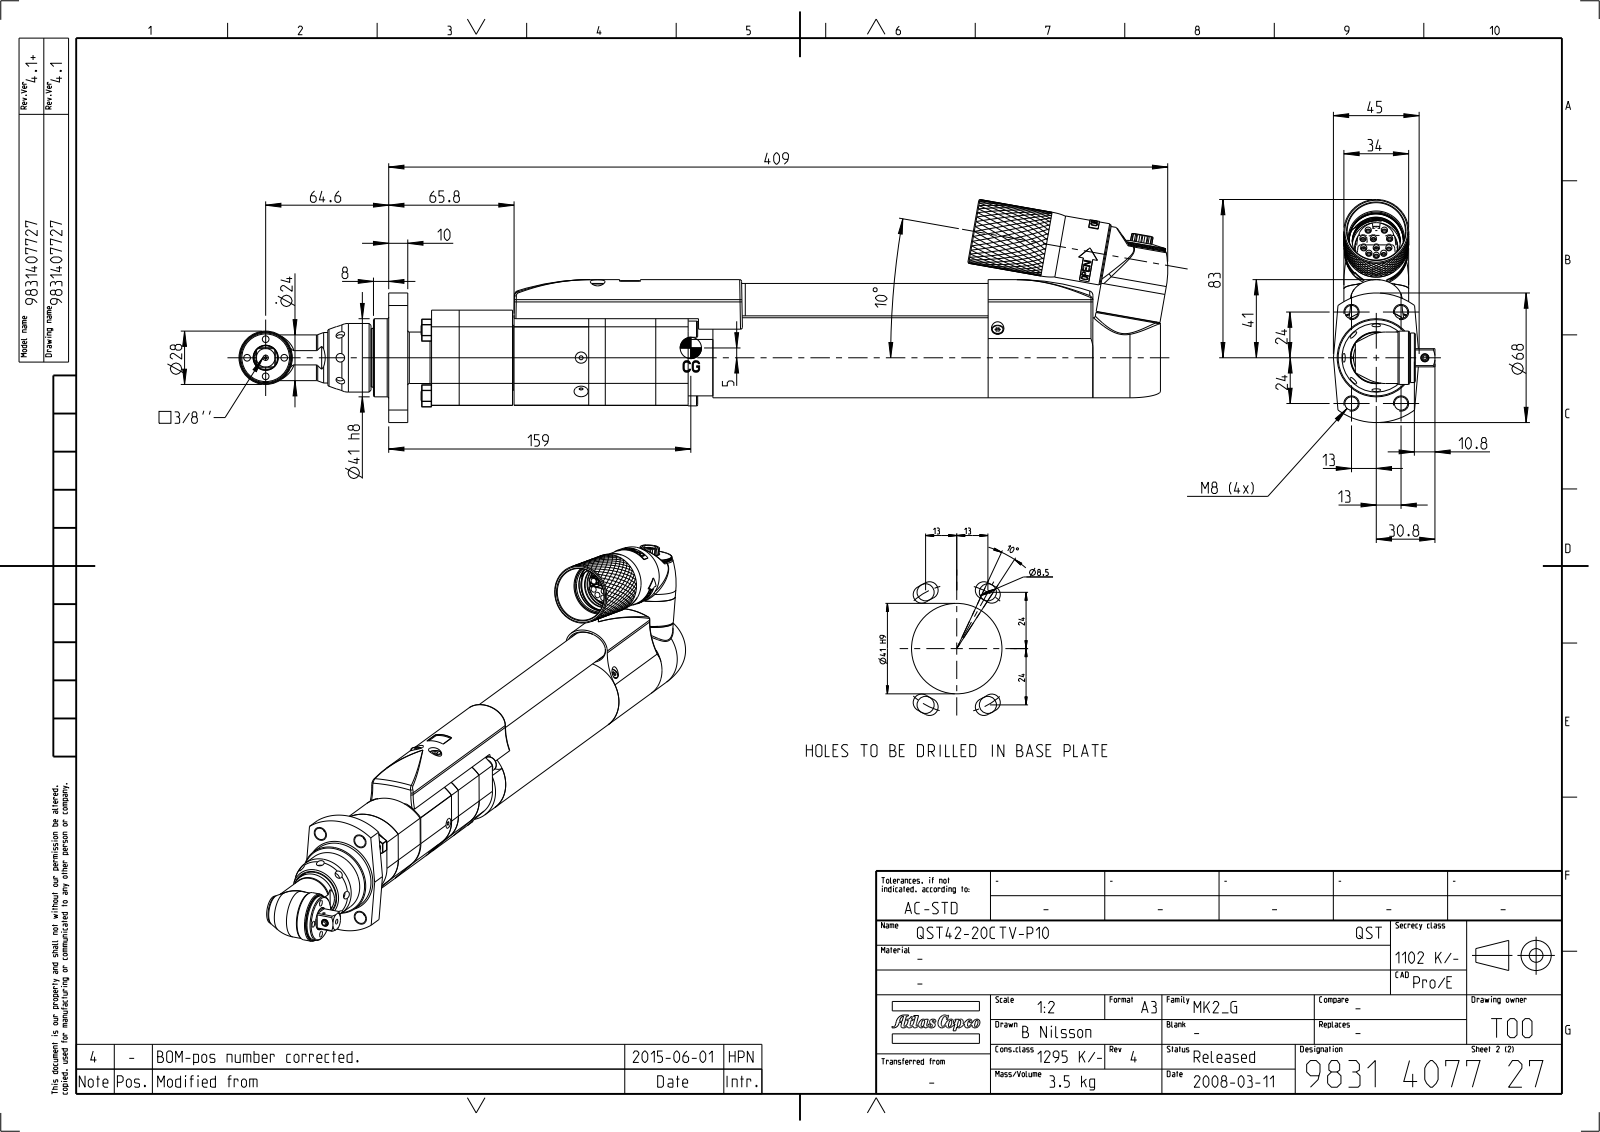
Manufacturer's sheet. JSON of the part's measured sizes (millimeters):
{"part_name": "4230260102; 4230260112_ASM; 4230262500; 0219110017 (+8 more)", "step_written_by": "CREO PARAMETRIC BY PTC INC, 2014500 (CONFIG_CONTROL_DESIGN)", "units": "millimeters", "bodies": {"solids": 38, "faces": 3554, "planar": 1340, "cylindrical": 1206, "other": 1008}, "overall_size": [487.61, 117.06, 53.3], "volume_mm3": 418272, "surface_area_mm2": 255683, "round_holes": [[3.3, 7], [3.5, 7], [4.5, 6], [2.46, 5], [3.24, 5], [7, 5], [1.5, 4], [8, 4], [1.4, 3], [2.94, 3], [4.13, 3], [4.3, 3]], "round_bosses_or_shafts": [[3, 7], [34, 5], [6, 5], [5, 5], [4, 5], [8.5, 3], [7, 3], [2.5, 3]], "partial_cylinders_radius": [[0.2, 32], [0.5, 21], [0.29, 12], [0.51, 12], [2, 9], [1, 7], [5.25, 4], [40, 4]], "face_to_face_distances": [38, 30, 160.2, 8, 26.5, 3.5, 113.7, 27, 37, 10], "hole_center_spacings": [15.92, 15, 9.22, 9.75, 13.6, 13.79, 15.26, 15.81]}
